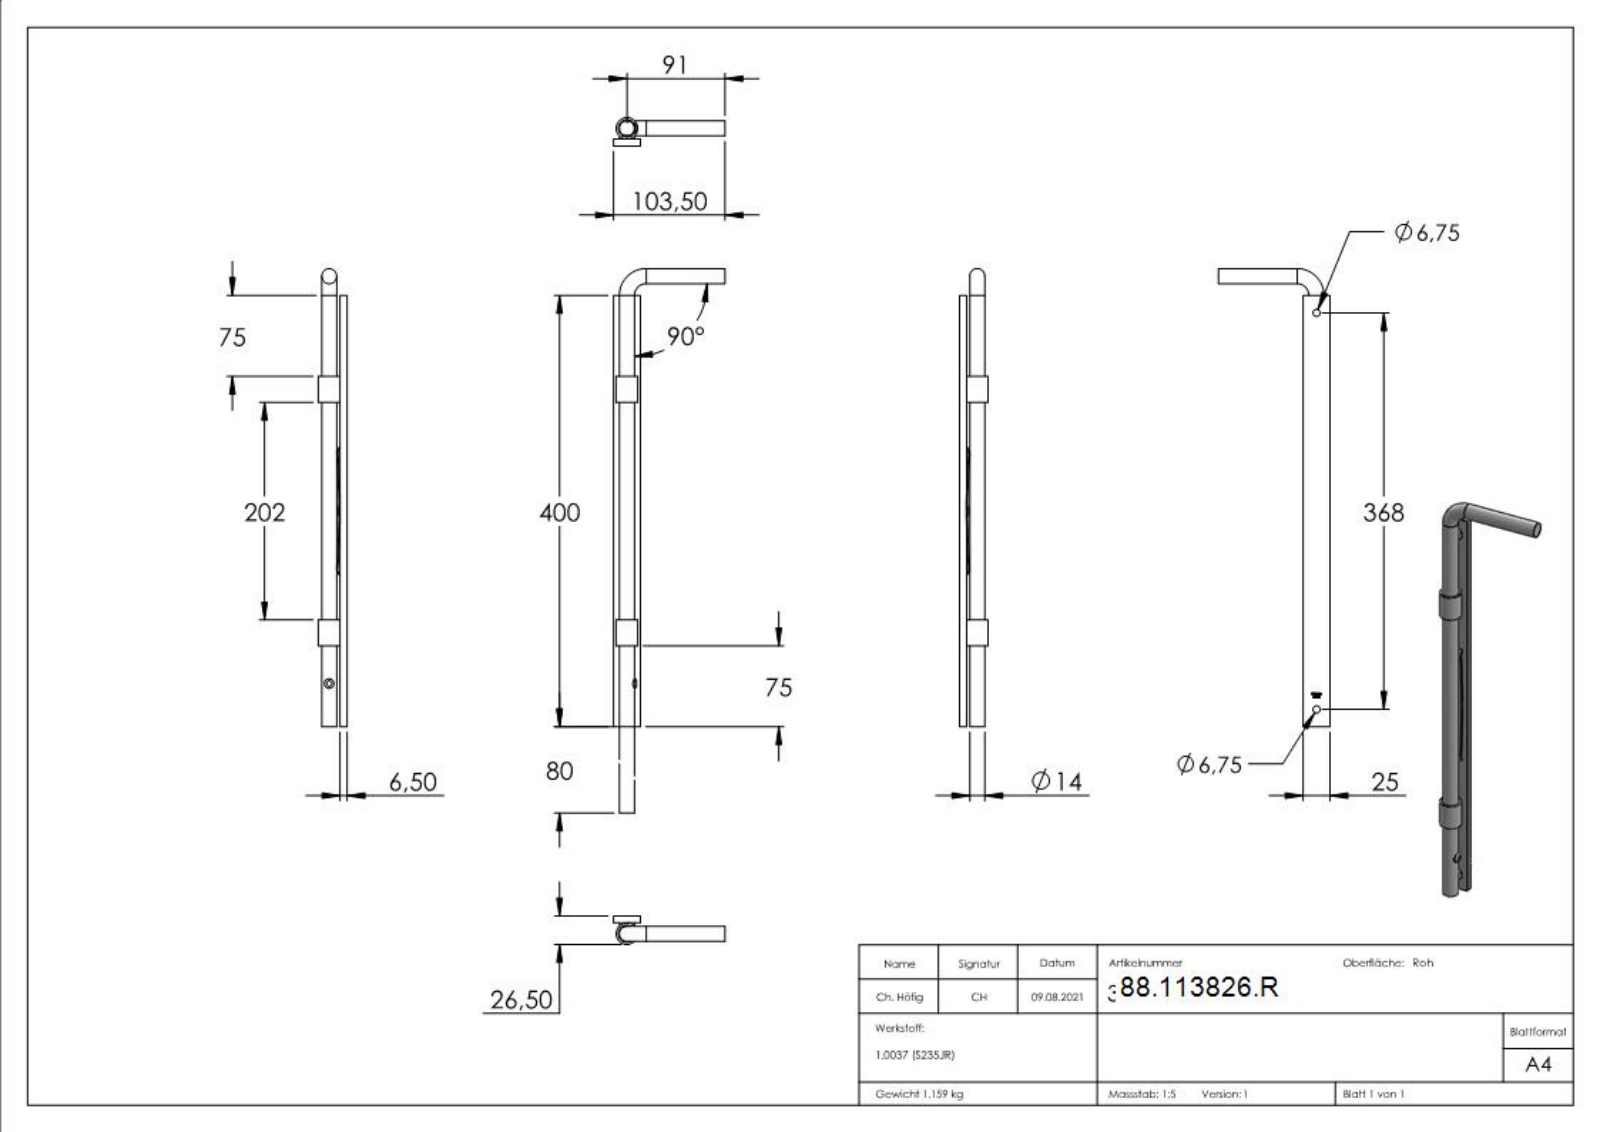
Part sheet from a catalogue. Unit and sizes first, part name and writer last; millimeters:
Units: millimetres
Overall size (bounding box): 425 × 103.5 × 26.5
Round holes (diameter × count): ⌀6.75 ×2, ⌀16 ×1
Round bosses / shafts (diameter × count): ⌀14 ×2, ⌀20 ×1, ⌀9 ×1, ⌀7 ×1
Partial cylindrical surfaces — rounded edges, fillets, slot ends (radius × count): R6.86 ×1, R8.67 ×1, R8.89 ×1, R9.67 ×1, R703.37 ×1, R704.37 ×1
Main face-to-face distances: 6.5, 25, 5.5, 19.5, 75, 99, 301, 325, 24, 226
Hole centre spacings: 368
Volume: 148 617 mm³ · Surface area: 57 590 mm²
Bodies: 5 solids, 240 faces (120 planar, 17 cylindrical, 103 other)
Part name (STEP PRODUCT): 3826-R
STEP written by: SolidWorks 2018 (CONFIG_CONTROL_DESIGN)
